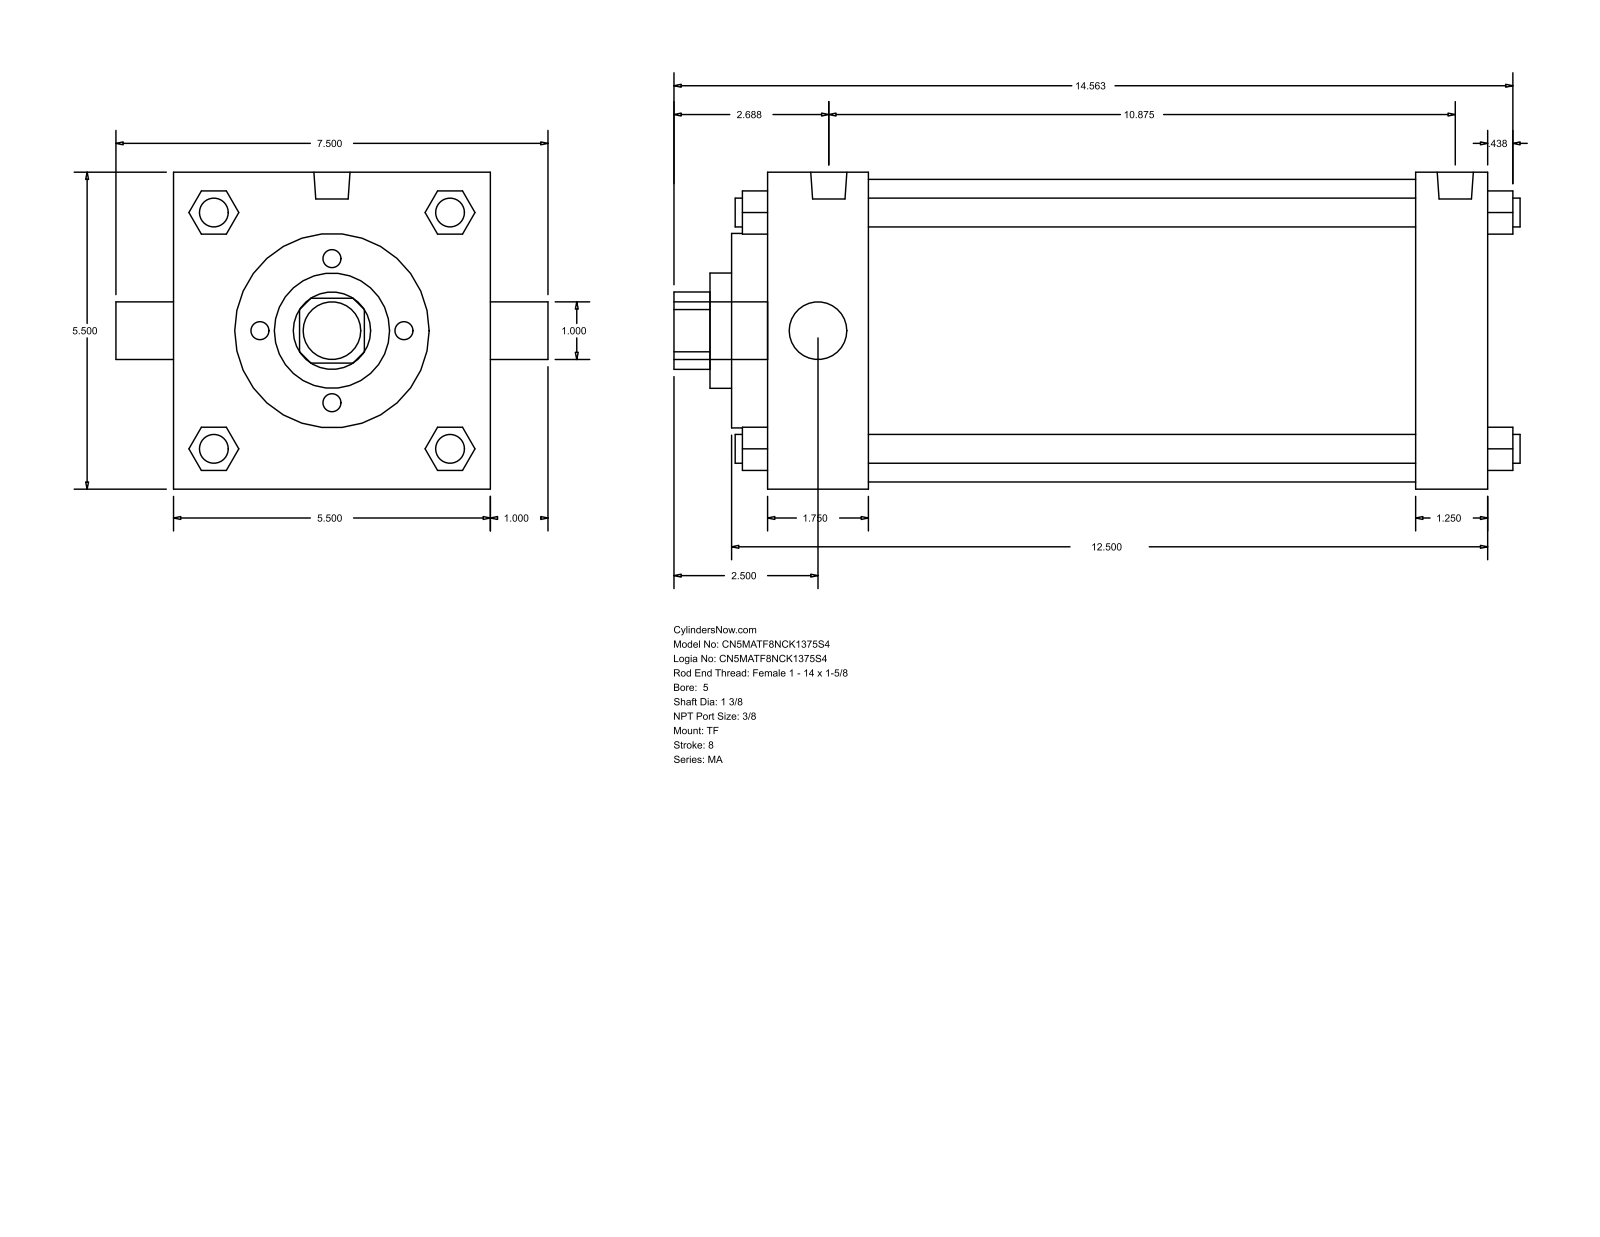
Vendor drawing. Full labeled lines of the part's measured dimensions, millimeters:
Part name (STEP PRODUCT): MA_TF__0500_1.375
STEP written by: GSSL Pune (CONFIG_CONTROL_DESIGN)
Units: millimetres
Bodies: 0 solids, 122 faces (93 planar, 29 cylindrical, 0 other)
Overall size (bounding box): 373.06 × 190.5 × 139.7
Round holes (diameter × count): ⌀25.4 ×1, ⌀34.92 ×1, ⌀50.8 ×1, ⌀85.72 ×1, ⌀133.35 ×1
Round bosses / shafts (diameter × count): ⌀12.7 ×4, ⌀11.11 ×3, ⌀15.93 ×2, ⌀25.4 ×1
Partial cylindrical surfaces — rounded edges, fillets, slot ends (radius × count): R17.06 ×1
Main face-to-face distances: 139.7, 317.5, 285.75, 31.75, 44.45, 241.3, 273.05, 15.87, 60.32, 301.62
